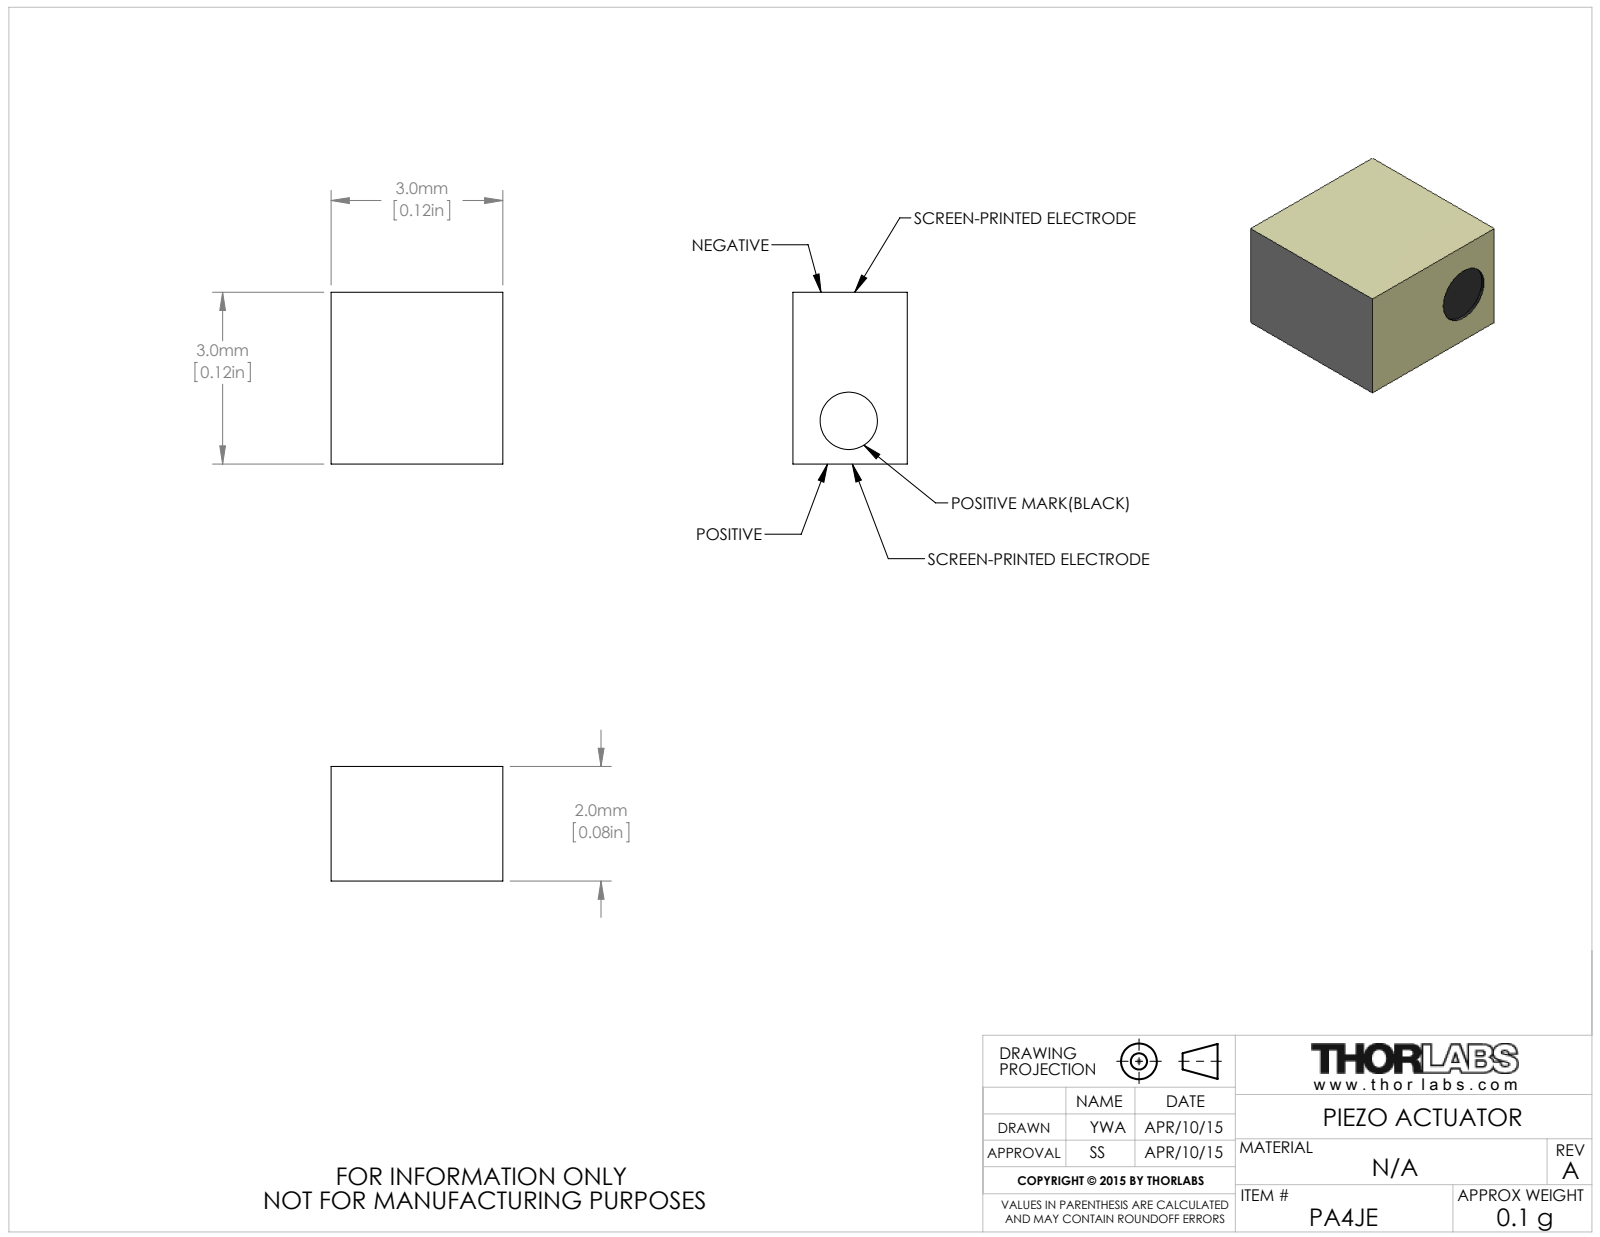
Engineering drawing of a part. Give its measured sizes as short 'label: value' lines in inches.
name: CTN002955
written by: SolidWorks 2014 (AUTOMOTIVE_DESIGN)
unit: in
bodies: 1 solid, 9 faces (7 planar, 2 cylindrical, 0 other)
size: 0.118 × 0.118 × 0.079
volume: 0.001 in³; area: 0.065 in²
holes: 1× ⌀0.039
face distances: 0.118, 0.079, 0.116
